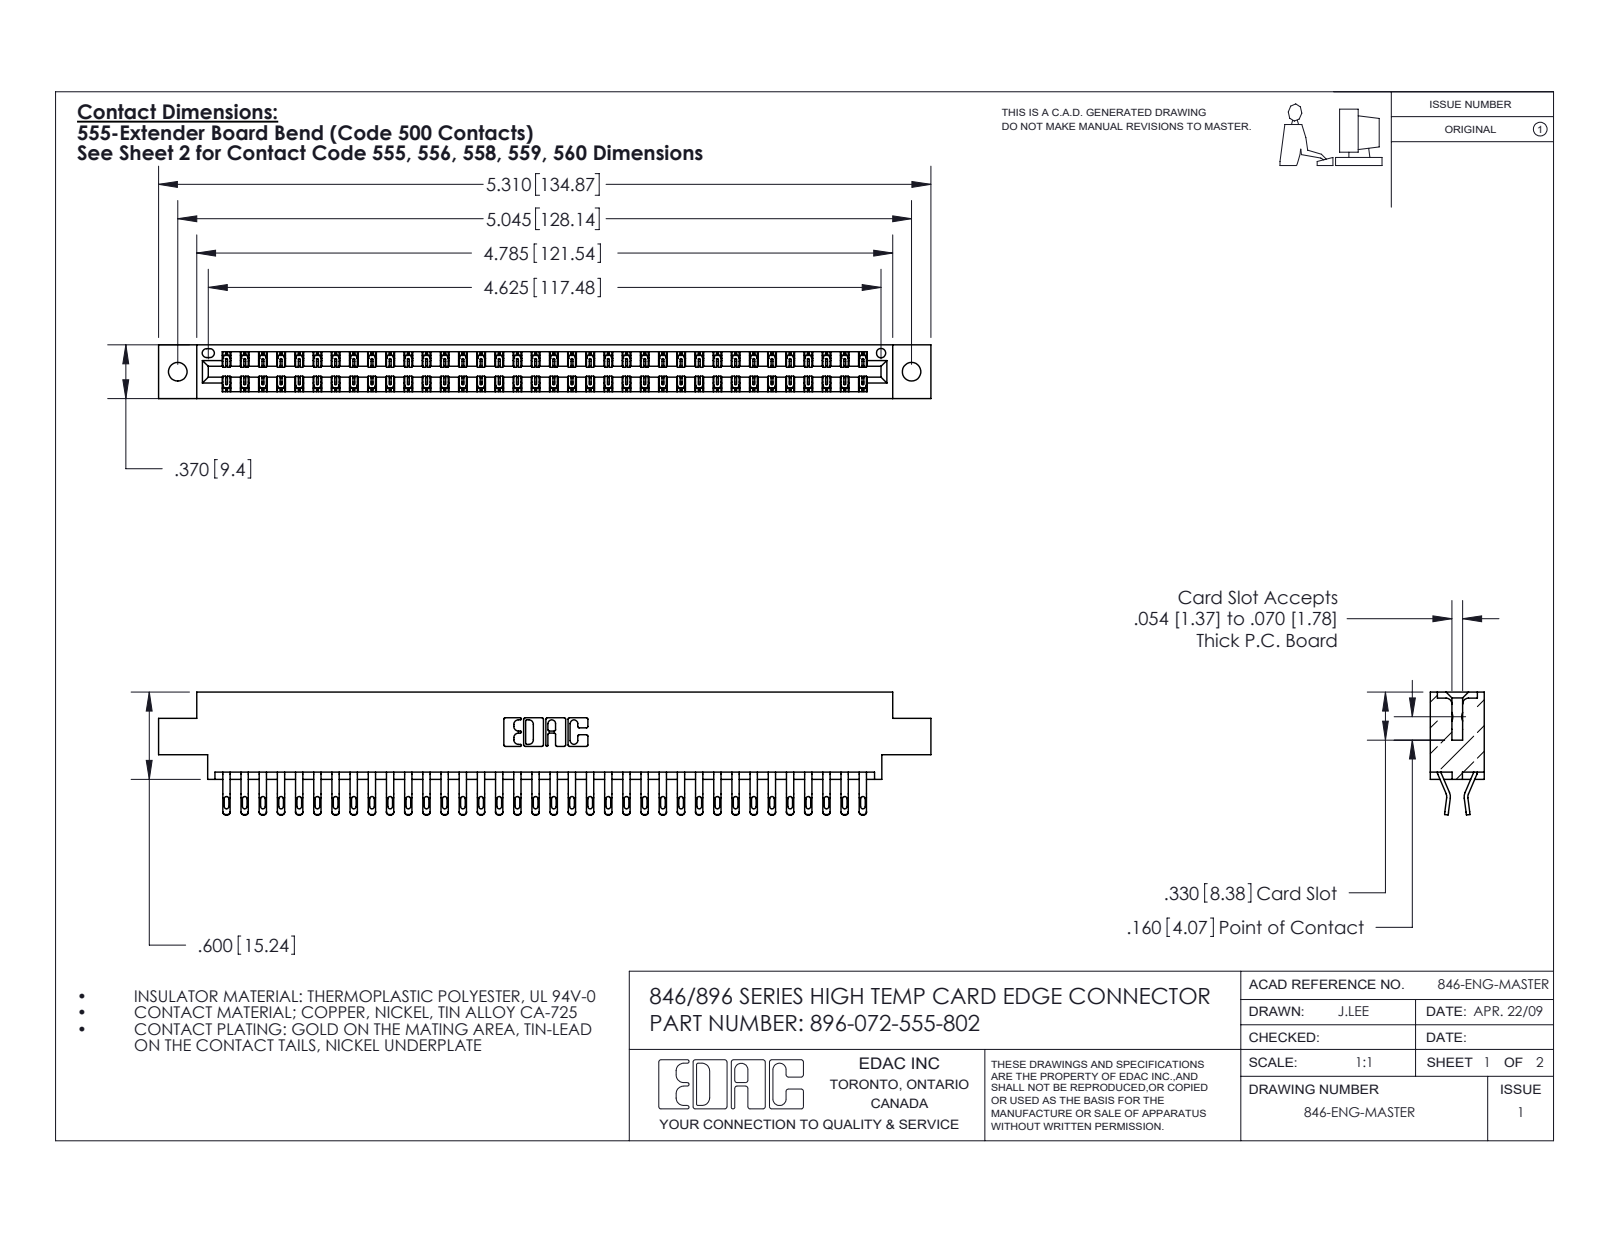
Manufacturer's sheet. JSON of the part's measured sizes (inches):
{"part_name": "345-292-001_555 Tail; 396-072-555-802; 346 Part_0.170 Offset - 0.128 Dia", "step_written_by": "SolidWorks 2016 (CONFIG_CONTROL_DESIGN)", "units": "inches", "bodies": {"solids": 73, "faces": 4302, "planar": 2456, "cylindrical": 1846, "other": 0}, "overall_size": [5.31, 0.845, 0.37], "volume_in3": 0.801, "surface_area_in2": 28.83, "round_holes": [[0.128, 2], [0.064, 1]], "partial_cylinders_radius": [[0.016, 144], [0.02, 144], [0.006, 108], [0.01, 22], [0.007, 6], [0.031, 6], [0.026, 3], [0.01, 2]], "face_to_face_distances": [0.048, 0.322, 0.37, 0.25, 0.025, 0.072, 0.298, 0.275, 0.148, 0.222], "hole_center_spacings": [0.246, 4.836, 5.045]}
